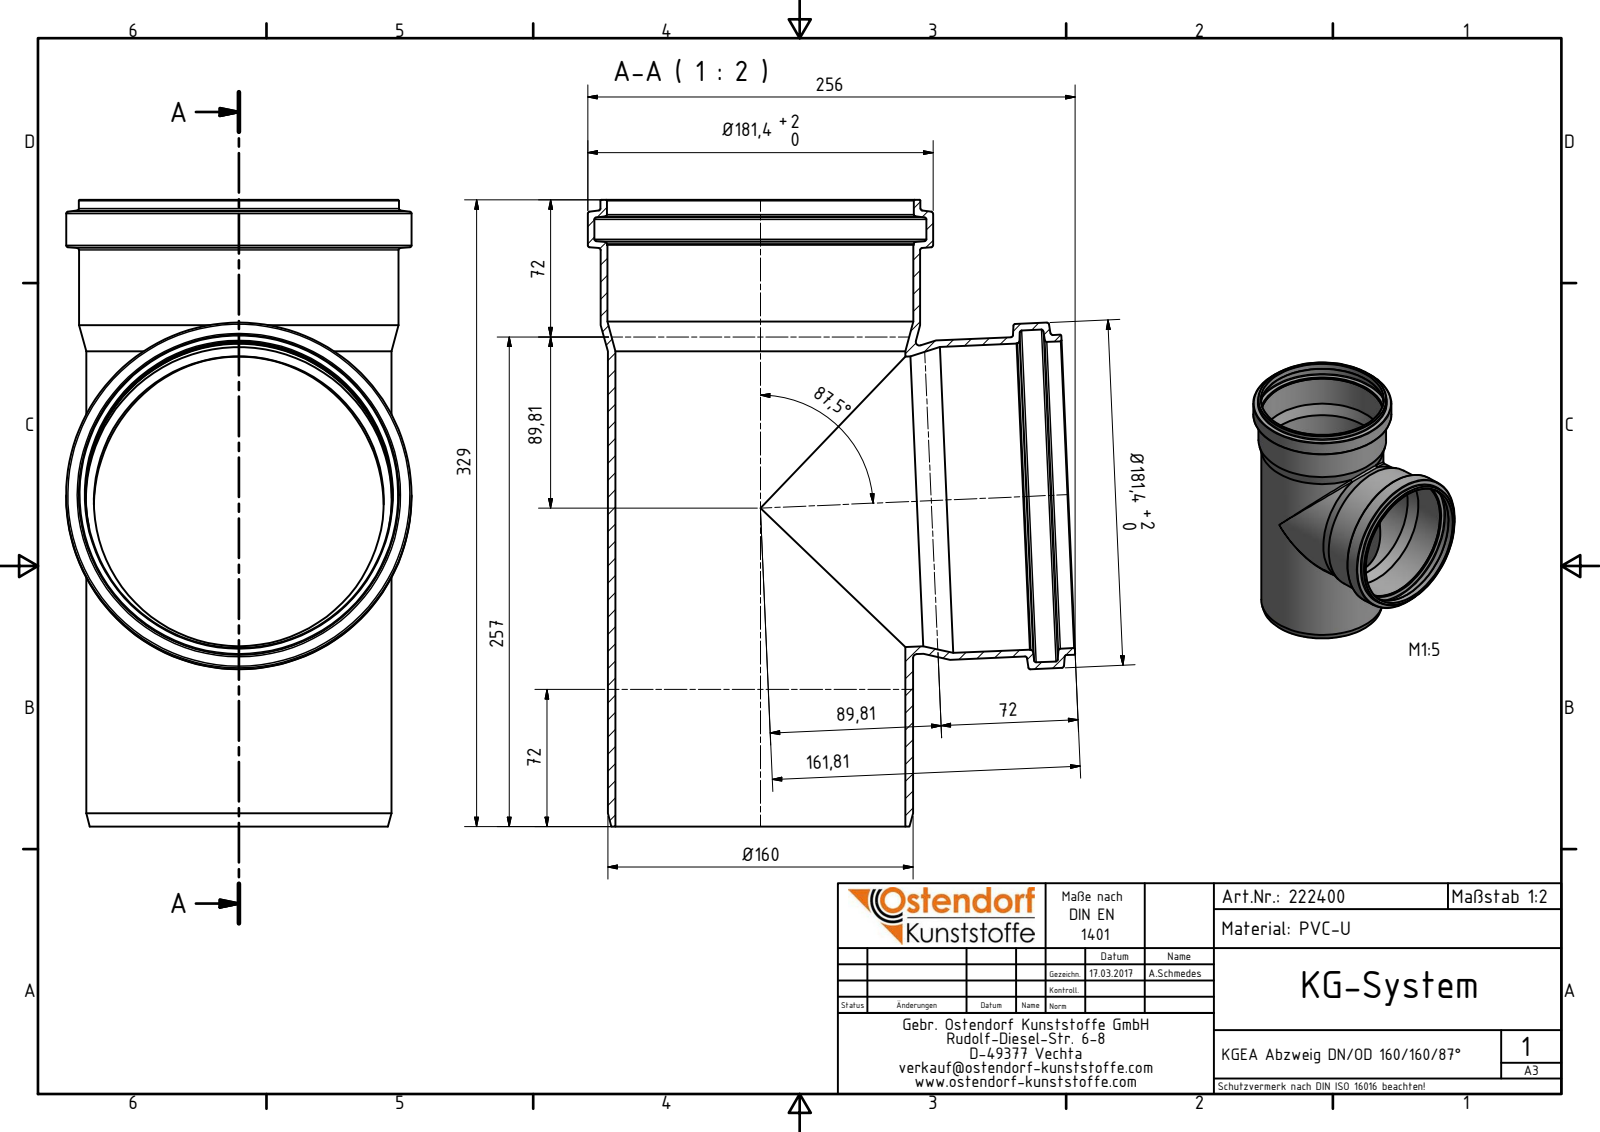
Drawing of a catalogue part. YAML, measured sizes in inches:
part_name: "222400 KGEA Abzweig DN_OD 160_160_87°"
step_written_by: "Autodesk Inventor 2016 (AUTOMOTIVE_DESIGN)"
units: inches
bodies: {solids: 1, faces: 60, planar: 5, cylindrical: 18, other: 37}
overall_size: [12.953, 10.079, 7.142]
volume: 48.6
surface_area: 654.8
round_holes:
  - {diameter: 6.343, count: 3}
  - {diameter: 5.996, count: 2}
  - {diameter: 6.327, count: 2}
  - {diameter: 6.866, count: 2}
round_bosses_or_shafts:
  - {diameter: 7.142, count: 2}
  - {diameter: 6.618, count: 2}
  - {diameter: 6.602, count: 2}
  - {diameter: 6.311, count: 2}
face_to_face_distances: [12.953, 0.929, 12.024]
